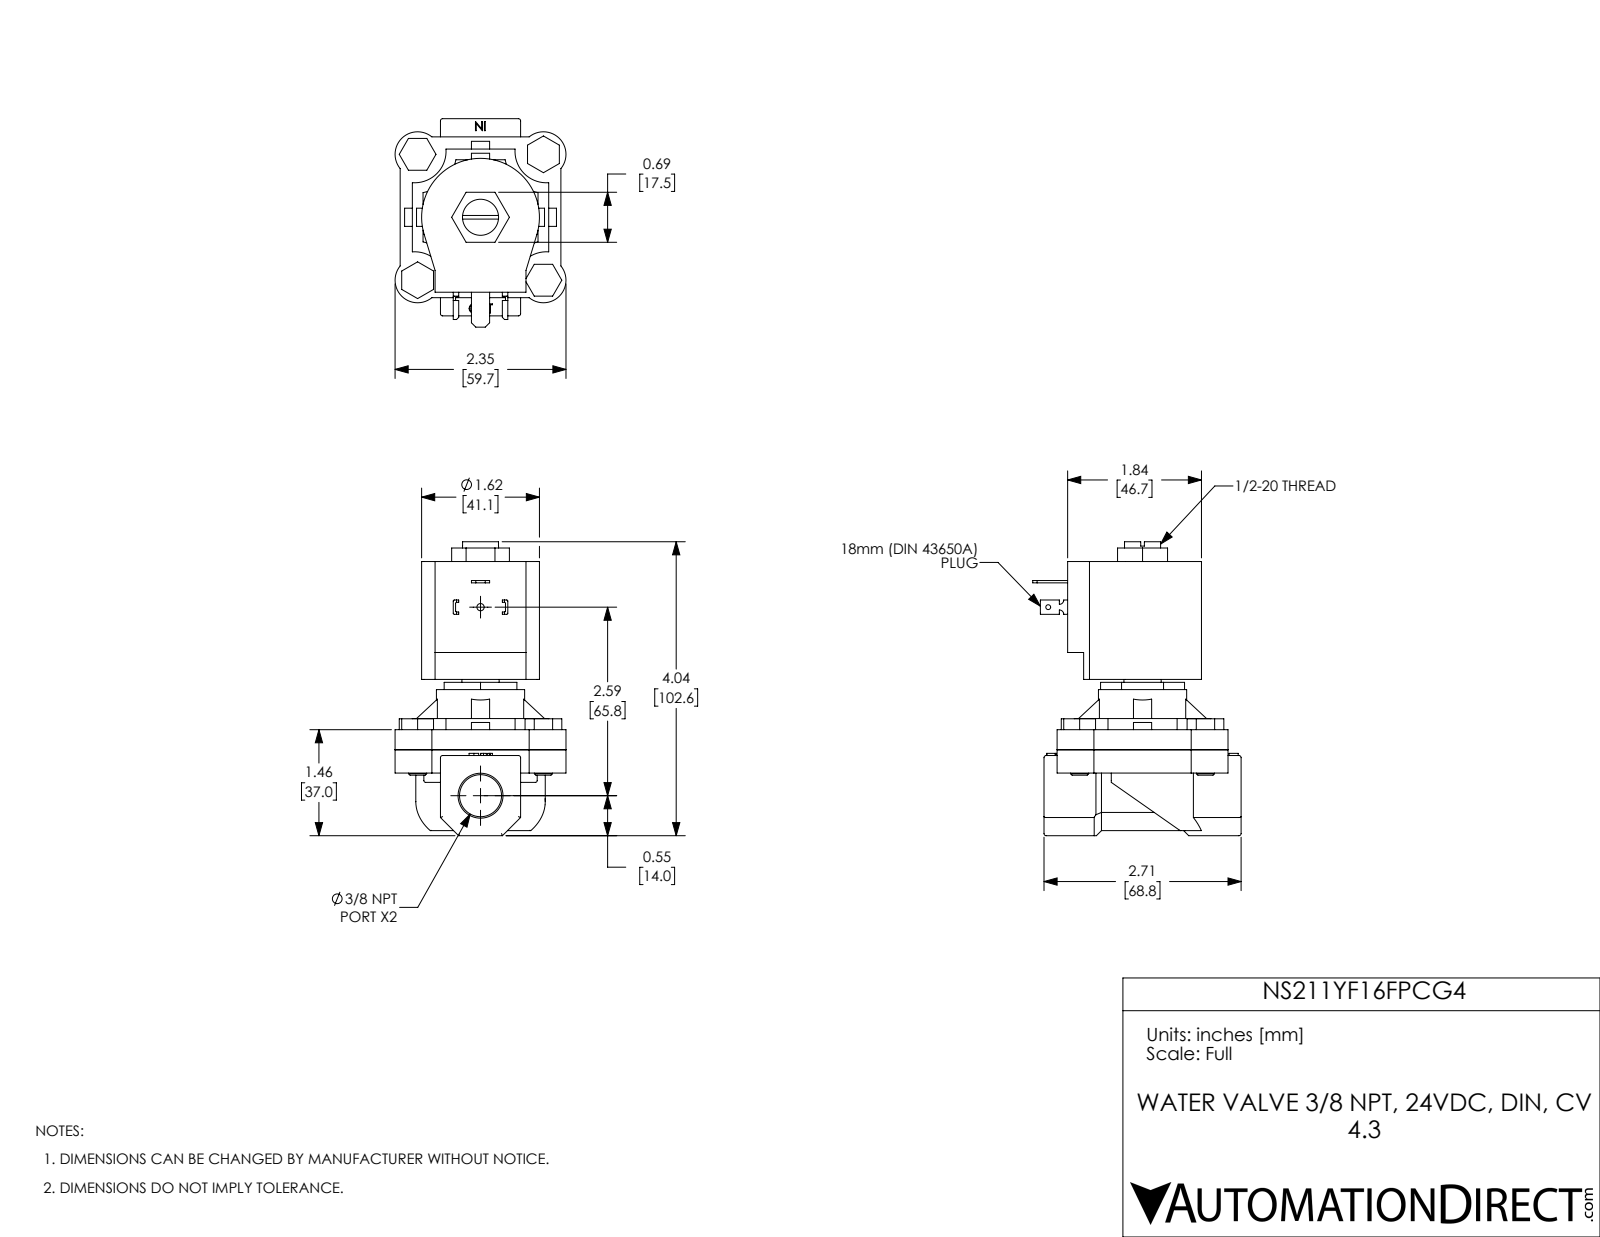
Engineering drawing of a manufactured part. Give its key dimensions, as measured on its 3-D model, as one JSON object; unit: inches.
{"part_name": "NS211YF16FPCG4", "step_written_by": "SolidWorks 2017 (AUTOMOTIVE_DESIGN)", "units": "inches", "bodies": {"solids": 11, "faces": 383, "planar": 237, "cylindrical": 113, "other": 33}, "overall_size": [4.04, 2.865, 2.35], "volume_in3": 10.3, "surface_area_in2": 66.77, "round_holes": [[0.25, 4], [0.067, 1], [0.1, 1], [0.496, 1], [0.512, 1], [0.578, 1], [1.155, 1]], "round_bosses_or_shafts": [[0.248, 4], [1.213, 1]], "partial_cylinders_radius": [[0.03, 15], [0.015, 8], [0.31, 4], [0.432, 4], [0.579, 4], [0.06, 2], [0.81, 1], [0.89, 1]], "face_to_face_distances": [0.276, 2.587, 2.311, 0.32, 0.596, 2.907, 0.554, 1.656, 0.25, 2.21], "hole_center_spacings": [1.223, 1.73, 2.446, 2.591]}
